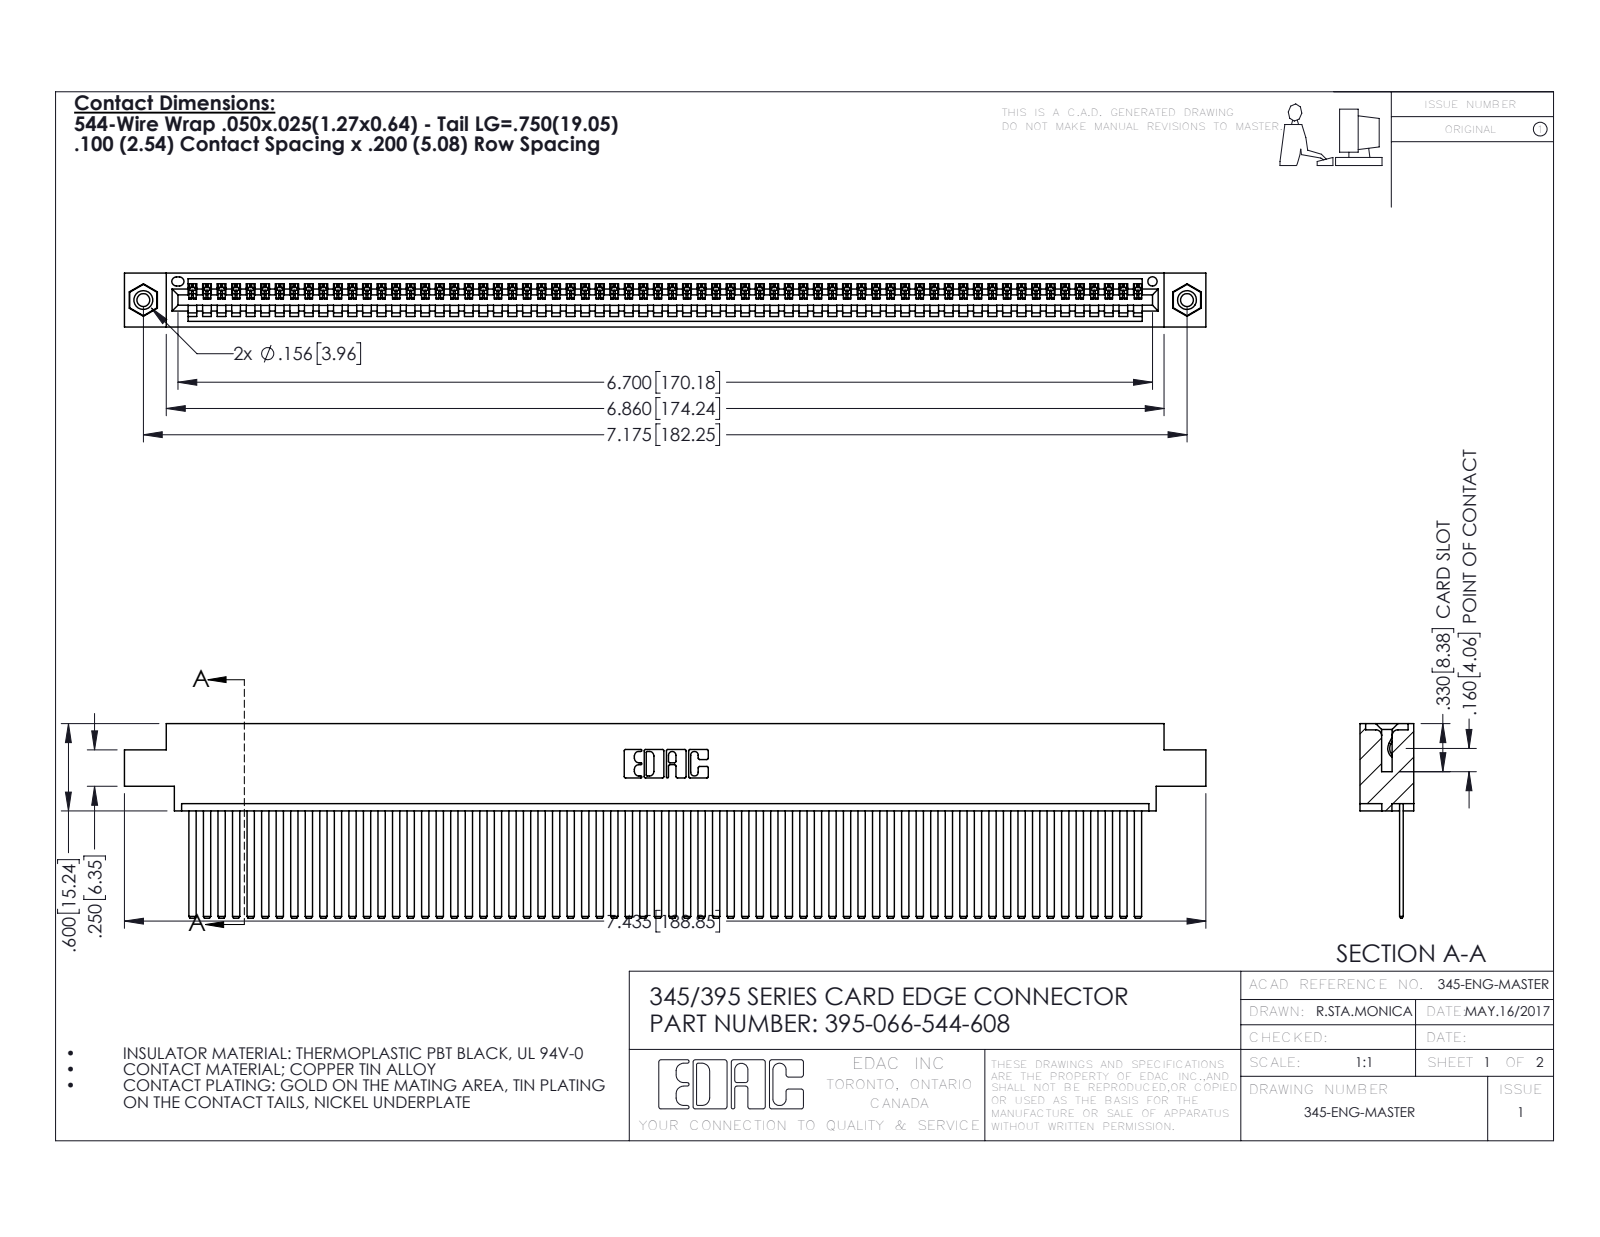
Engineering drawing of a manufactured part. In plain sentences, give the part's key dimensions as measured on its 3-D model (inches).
The part is named "345 Part_0.170 Offset - 0.156 Dia-TI; 345-250-001_345-250-003-102; 345-292-001_345-293-144; 395-066-544-608". Its 3-D file was written by "SolidWorks 2016 (CONFIG_CONTROL_DESIGN)". It is 69 solids with 3622 faces: 2492 planar, 1114 cylindrical and 16 other. Overall it measures 7.435 by 1.337 by 0.37 inches. Its volume is 1.146 cubic inches and its surface area 42.97 square inches. Round holes: 2 of diameter 0.089, 2 of diameter 0.125, 2 of diameter 0.156, 1 of diameter 0.064. Round bosses or shafts: 2 of diameter 0.155. Partial cylindrical surfaces (rounded edges, fillets, slot ends): 132 of radius 0.006, 22 of radius 0.01, 6 of radius 0.007, 6 of radius 0.031, 3 of radius 0.026, 2 of radius 0.031, 2 of radius 0.04, 1 of radius 0.014. The main face-to-face distances are 0.072, 0.298, 0.025, 0.098, 0.272, 0.37, 0.2, 0.225, 0.175, 0.149. The hole center spacings are 0.27, 6.939, 7.175.
